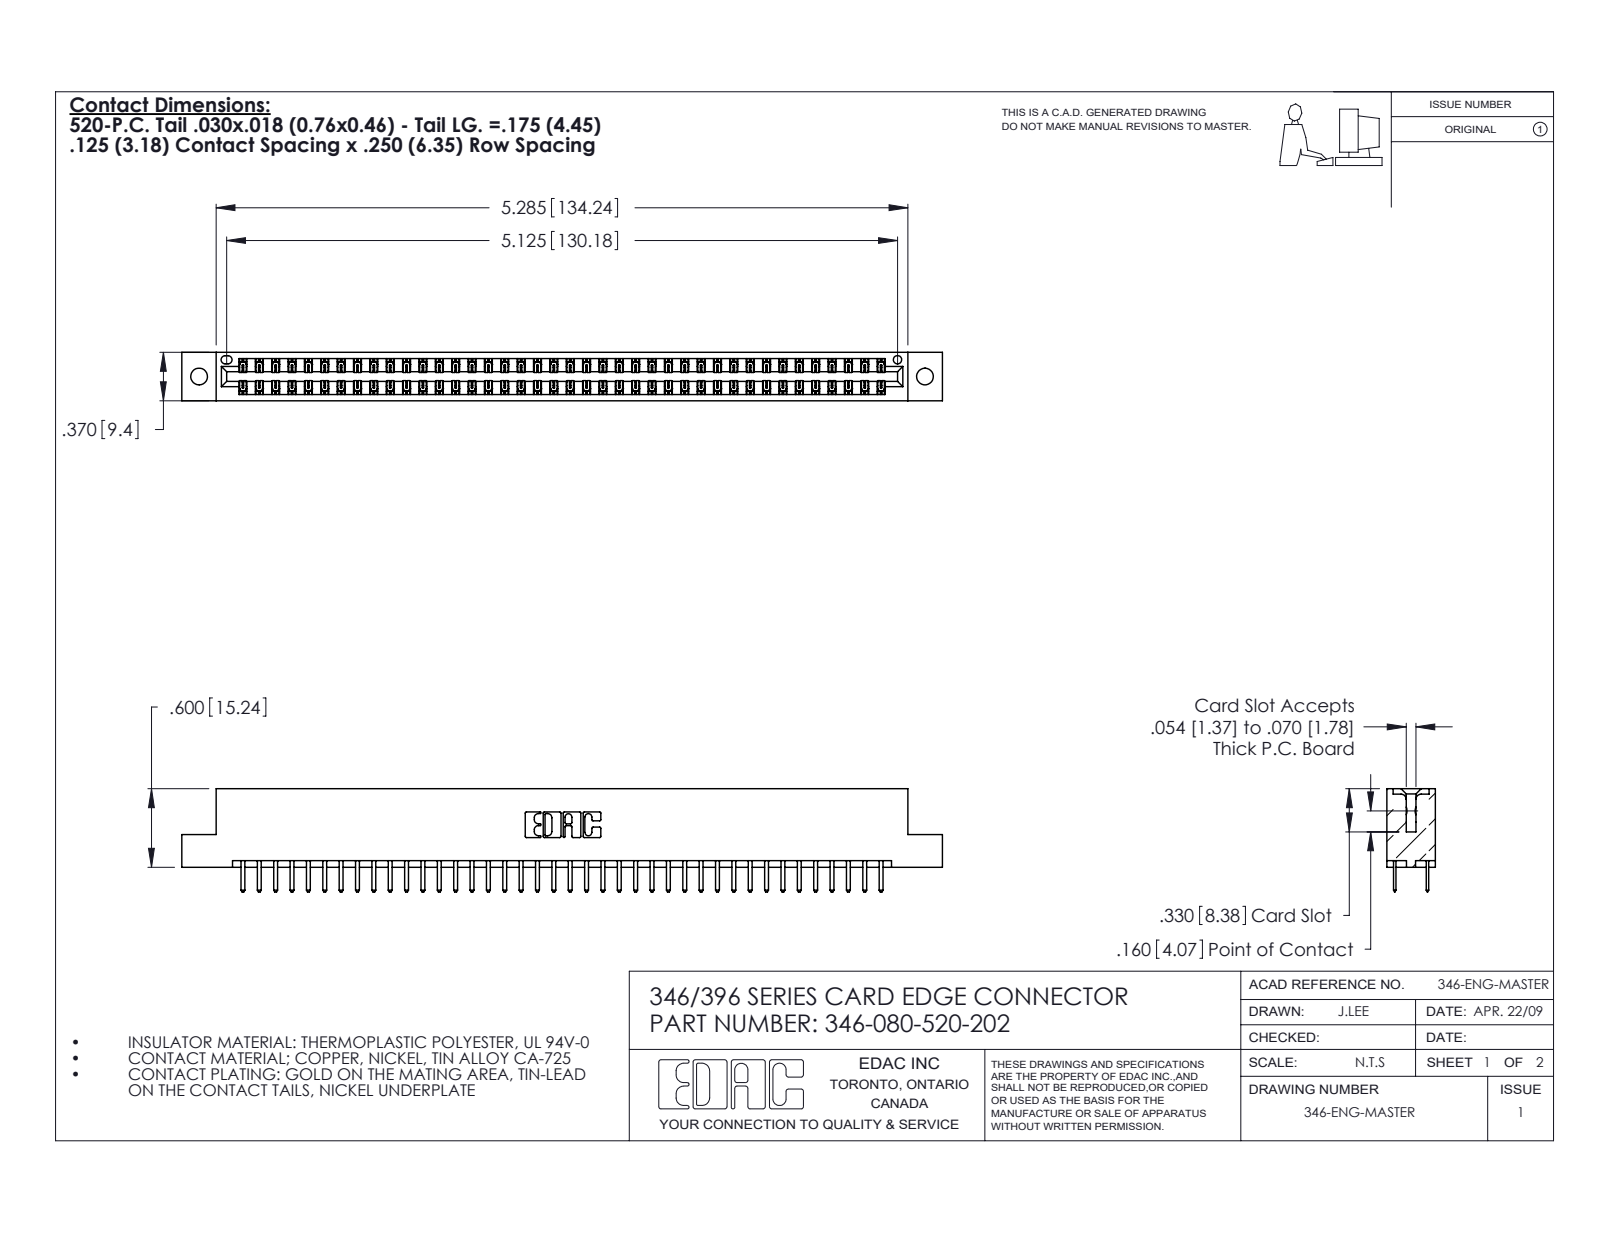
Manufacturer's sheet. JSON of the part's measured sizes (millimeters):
{"part_name": "346 Part_Flush Mounting Lugs - 0.128 Dia; 346-080-520-202; 345-292-001_345-293-120", "step_written_by": "SolidWorks 2020 (CONFIG_CONTROL_DESIGN)", "units": "millimeters", "bodies": {"solids": 81, "faces": 4602, "planar": 3036, "cylindrical": 1566, "other": 0}, "overall_size": [147.6, 20, 9.4], "volume_mm3": 14300, "surface_area_mm2": 19280, "round_holes": [[3.3, 2], [1.6, 1]], "partial_cylinders_radius": [[0.2, 120], [0.3, 84], [0.3, 22], [0.2, 6], [0.8, 6], [0.7, 3], [0.4, 2], [0.6, 2]], "face_to_face_distances": [1.2, 8.2, 6.4, 9.4, 7, 1.8, 7.6, 0.6, 3.8, 5.6], "hole_center_spacings": [6.2, 135.5, 140.8]}
